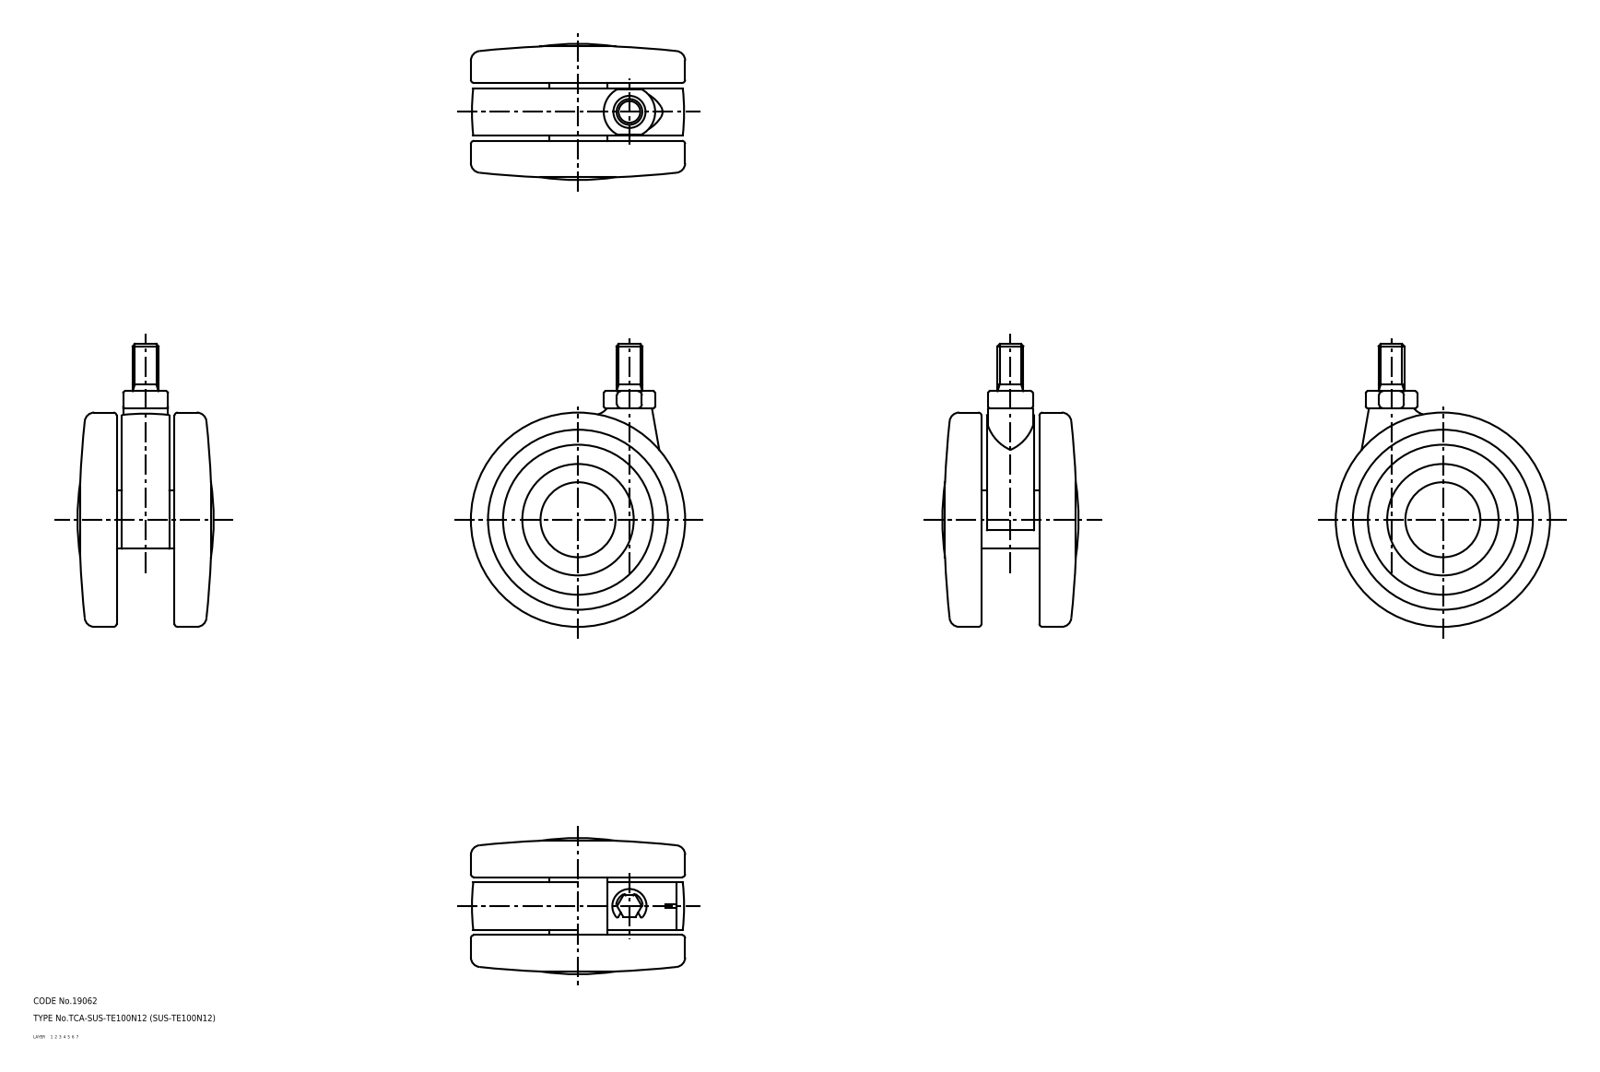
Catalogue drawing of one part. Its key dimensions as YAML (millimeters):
part_name: "wheel_mr; wheel; main shaft; SUS_TE100N12_4463_36"
step_written_by: "CADfix (AUTOMOTIVE_DESIGN)"
units: millimeters
bodies: {solids: 4, faces: 134, planar: 0, cylindrical: 0, other: 134}
overall_size: [132, 100, 63.57]
volume: 306390
surface_area: 71255
